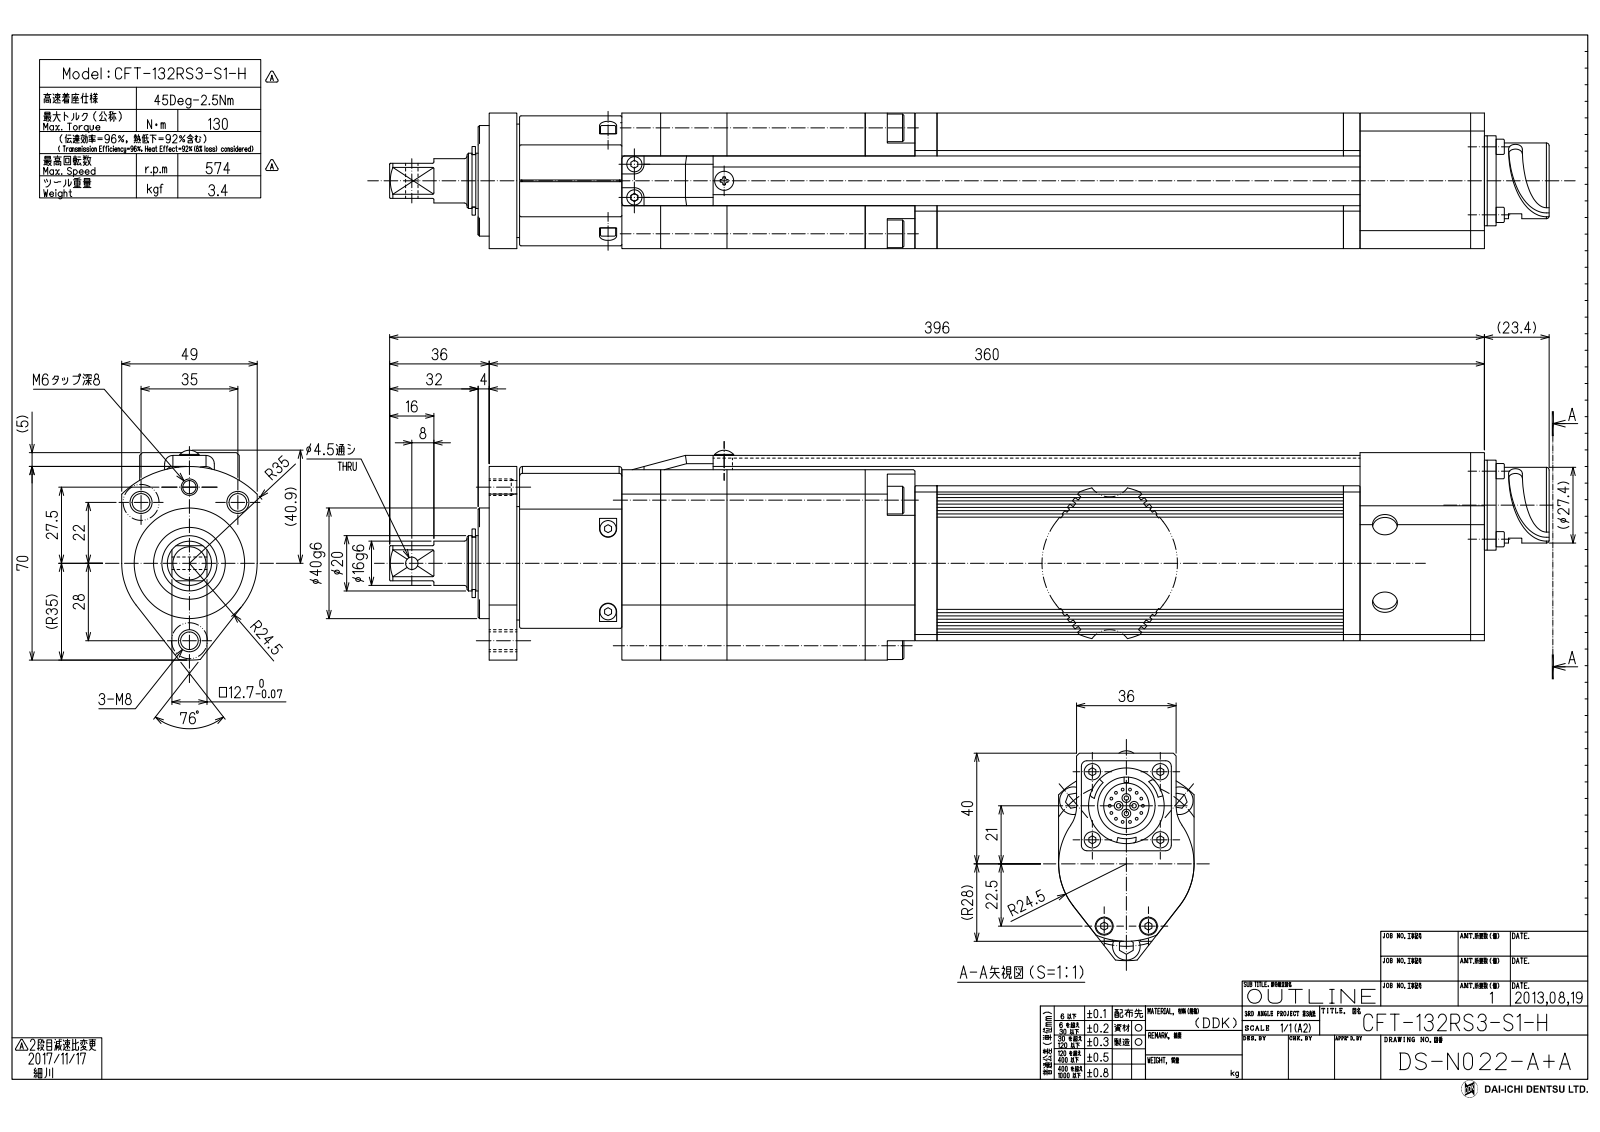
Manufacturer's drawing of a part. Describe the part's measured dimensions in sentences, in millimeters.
The part is named "CFT-132RS3-S1-H(DS-N022+C)_OUTLINE_20201124". Its 3-D file was written by "Autodesk Inventor 2021 (AUTOMOTIVE_DESIGN)". It is 1 solid with 667 faces: 439 planar, 143 cylindrical and 85 other. Overall it measures 419.4 by 75.84 by 49 millimeters. Its volume is 887 373 cubic millimeters and its surface area 99 099 square millimeters. Round holes: 4 of diameter 4.92, 4 of diameter 9, 3 of diameter 6.65, 2 of diameter 1.3, 2 of diameter 6.5, 1 of diameter 4.5, 1 of diameter 20.8, 1 of diameter 21. Round bosses or shafts: 14 of diameter 1, 10 of diameter 5.5, 4 of diameter 8, 4 of diameter 1.6, 3 of diameter 10, 1 of diameter 47, 1 of diameter 41, 1 of diameter 40. Partial cylindrical surfaces (rounded edges, fillets, slot ends): 6 of radius 2, 4 of radius 2.5, 4 of radius 3, 3 of radius 1, 3 of radius 5.5, 2 of radius 3.1, 2 of radius 3.5, 2 of radius 4. The main face-to-face distances are 1.5, 1, 49, 15.5, 33.5, 49.01, 0.5, 12, 3, 22. The hole center spacings are 1.88, 9.71, 10.83, 17.53, 18.34, 19.28, 19.77, 23.88.
